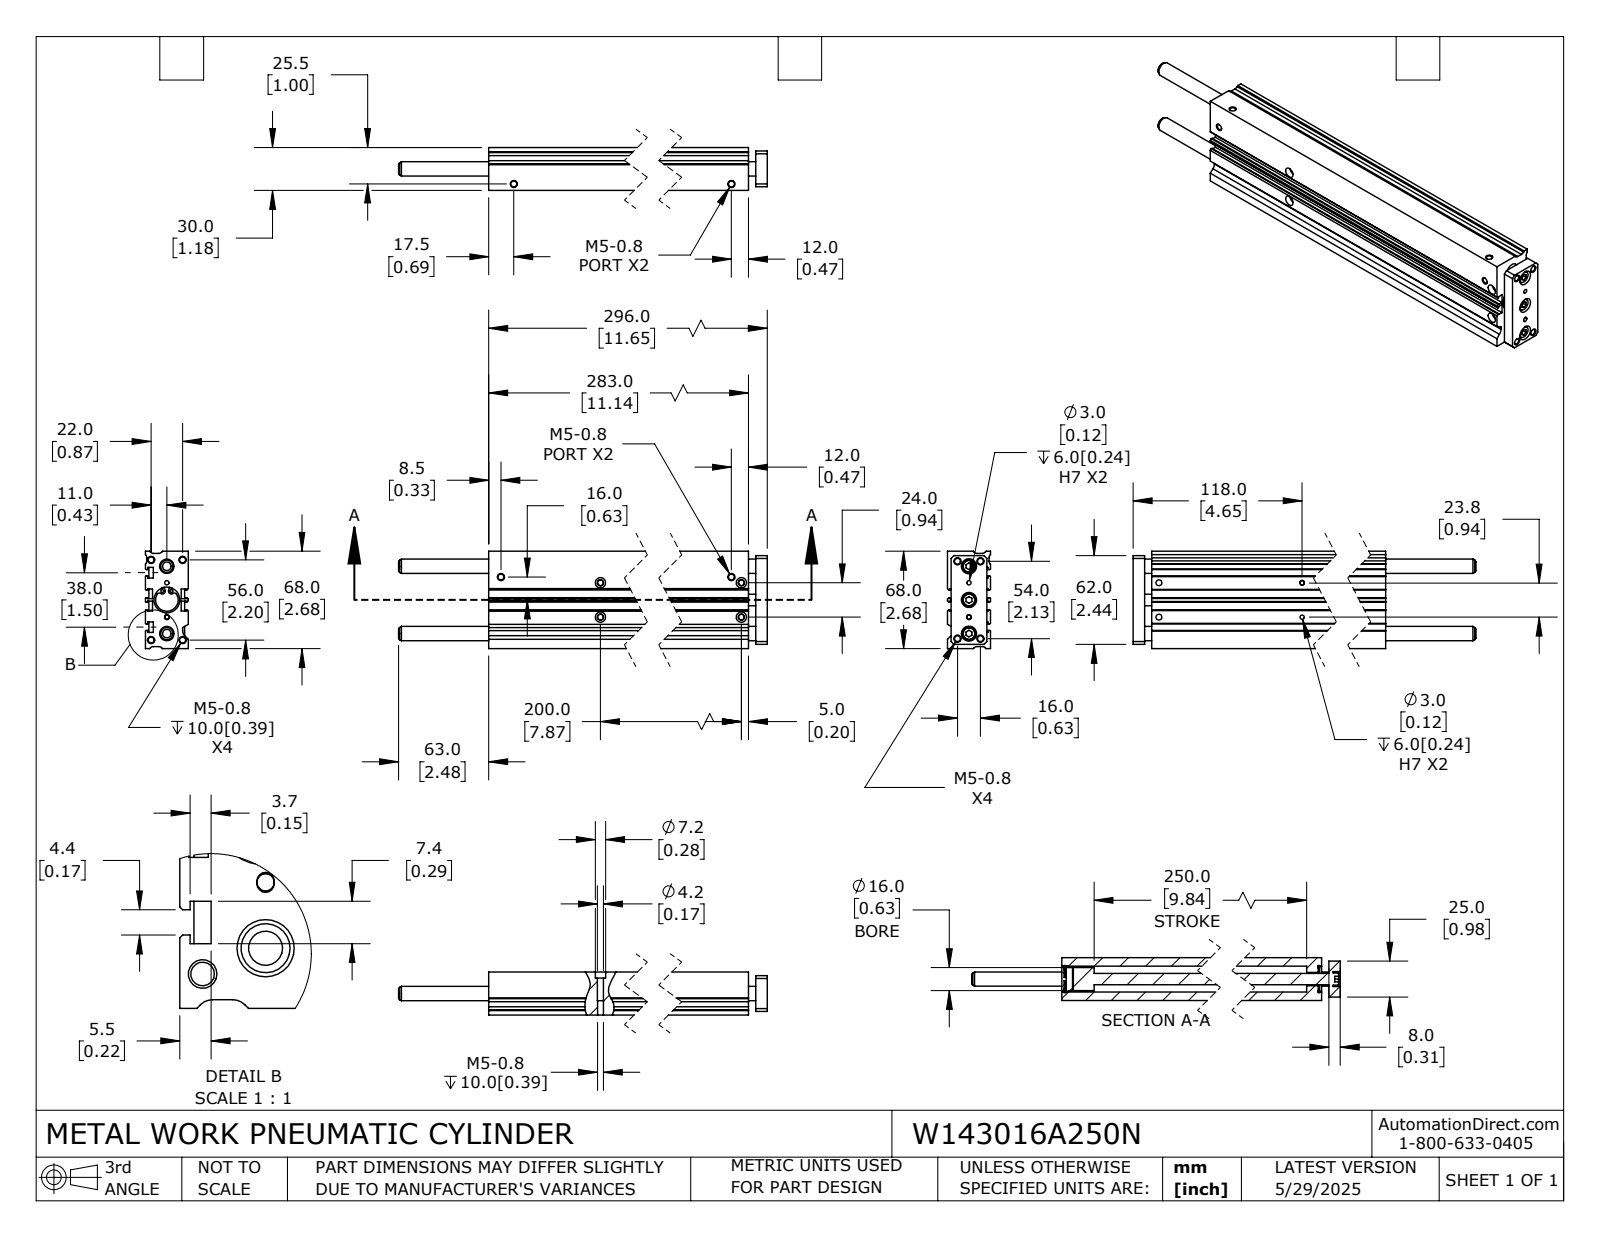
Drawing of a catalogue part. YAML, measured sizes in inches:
part_name: "W143016A250N_BODY; W143016A250N; W143016A250N_ROD"
step_written_by: "SolidWorks 2024 (CONFIG_CONTROL_DESIGN)"
units: inches
bodies: {solids: 5, faces: 344, planar: 169, cylindrical: 137, other: 38}
overall_size: [14.134, 2.677, 1.181]
volume: 28.71
surface_area: 242.4
round_holes:
  - {diameter: 0.163, count: 16}
  - {diameter: 0.079, count: 4}
  - {diameter: 0.118, count: 4}
  - {diameter: 0.165, count: 4}
  - {diameter: 0.283, count: 4}
  - {diameter: 0.413, count: 3}
  - {diameter: 0.394, count: 2}
  - {diameter: 0.362, count: 1}
  - {diameter: 0.618, count: 1}
  - {diameter: 0.709, count: 1}
round_bosses_or_shafts:
  - {diameter: 0.335, count: 3}
  - {diameter: 0.748, count: 2}
  - {diameter: 0.63, count: 1}
  - {diameter: 0.315, count: 1}
partial_cylinders:
  - {radius: 0.118, count: 6}
  - {radius: 0.059, count: 4}
  - {radius: 0.062, count: 4}
  - {radius: 0.081, count: 4}
  - {radius: 0.197, count: 1}
face_to_face_distances: [1.181, 0.197, 0.984, 2.677, 0.059, 0.217, 1.305, 0.965, 0.02, 0.768]
hole_center_spacings: [0.124, 0.261, 0.274, 0.344, 0.468, 0.669, 0.693, 0.727]
